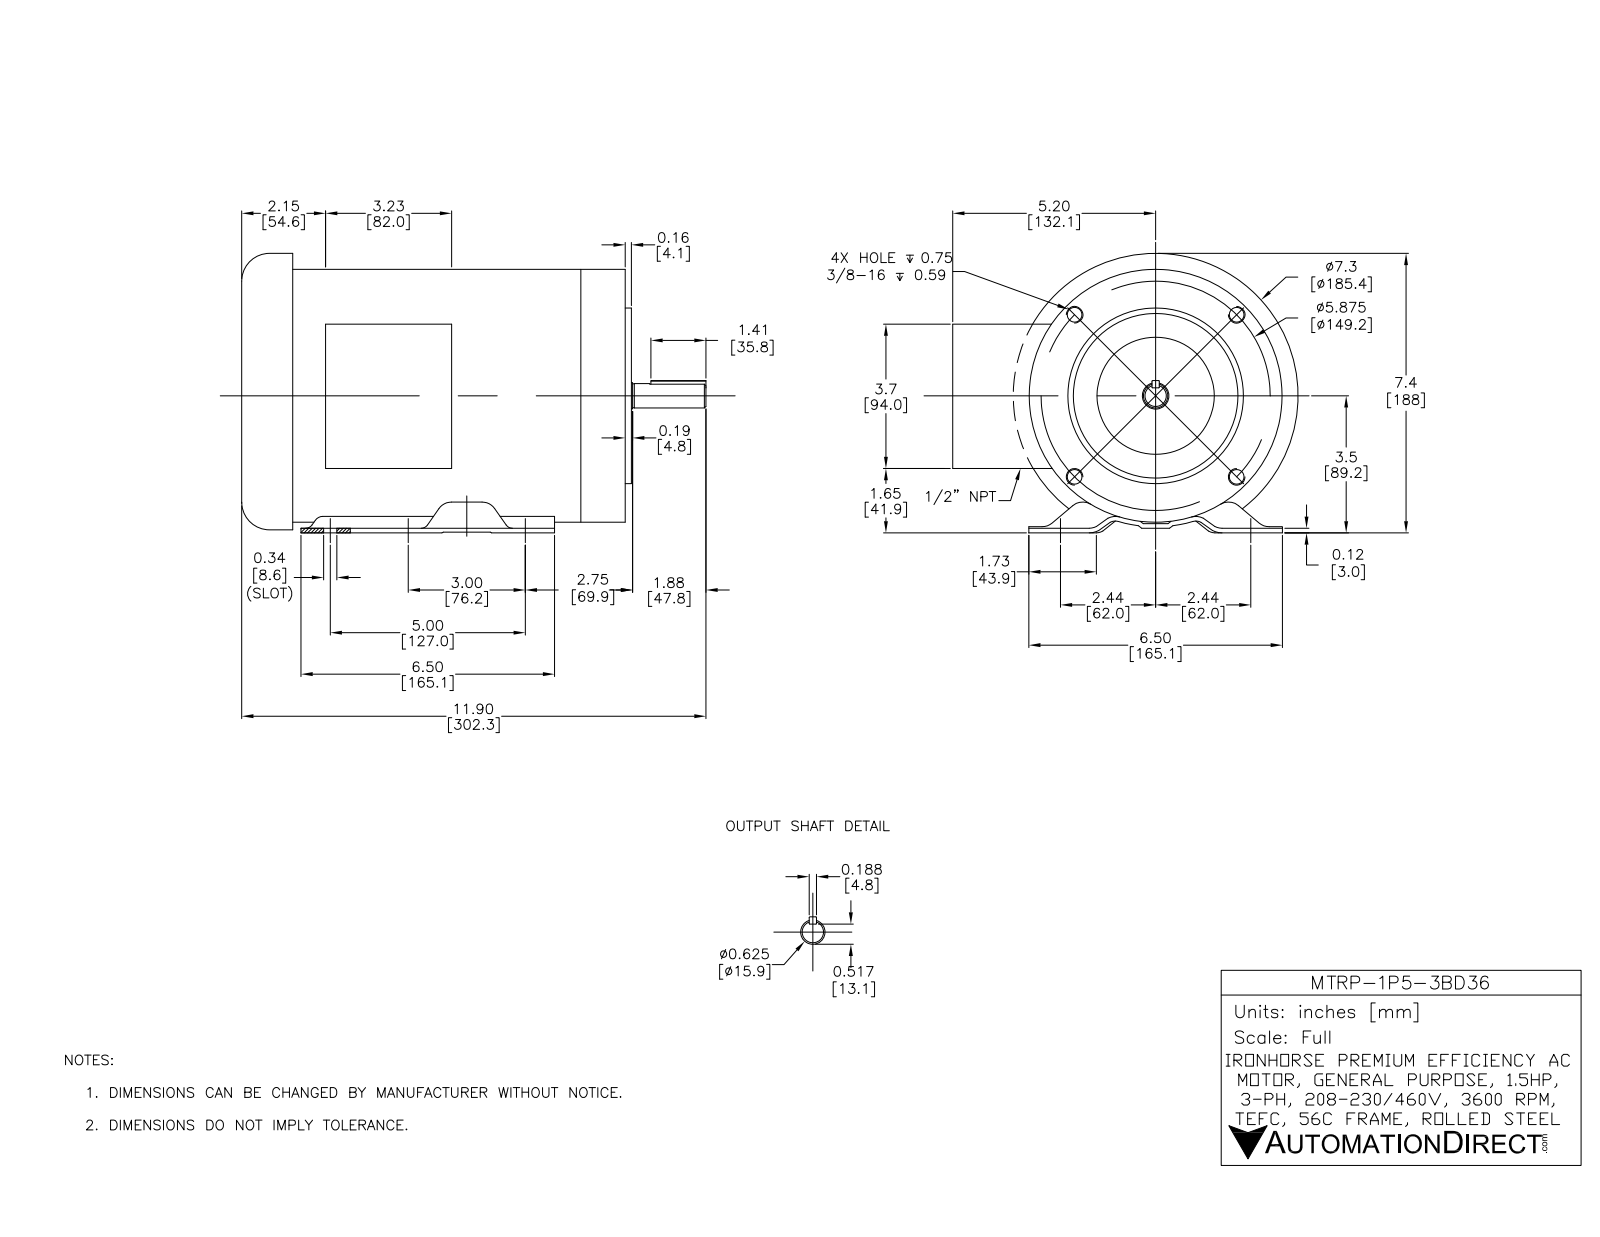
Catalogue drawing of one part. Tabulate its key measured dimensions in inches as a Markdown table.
| quantity | value |
| --- | --- |
| part name | MTRP-1P5-3BD36 |
| STEP written by | SolidWorks 2017 (AUTOMOTIVE_DESIGN) |
| units | inches |
| bodies | 39 solids, 3563 faces (797 planar, 1141 cylindrical, 1625 other) |
| overall size | 11.713 × 8.938 × 7.234 |
| volume | 44.24 in³ |
| surface area | 957.6 in² |
| round holes (diameter × count) | 0.197 × 12, 0.219 × 9, 0.276 × 8, 0.217 × 6, 0.273 × 6, 0.344 × 6, 0.136 × 5, 0.15 × 4, 0.177 × 4, 0.313 × 4, 0.067 × 2, 0.134 × 2 |
| round bosses / shafts (diameter × count) | 0.164 × 9, 0.348 × 7, 0.414 × 6, 0.25 × 6, 0.19 × 6, 0.348 × 2, 7.185 × 1, 6.457 × 1 |
| partial cylindrical surfaces (radius × count) | 0.02 × 204, 0.118 × 123, 0.079 × 43, 0.039 × 38, 0.157 × 32, 0.138 × 26, 0.276 × 19, 0.172 × 12 |
| main face-to-face distances | 0.118, 0.039, 0.063, 9.646, 9.606, 3.559, 0.079, 3.087, 0.047, 0.098 |
| hole center spacings | 4.221, 3.031, 0.094, 2.32, 2.409, 2.937, 2.979, 3.748 |
